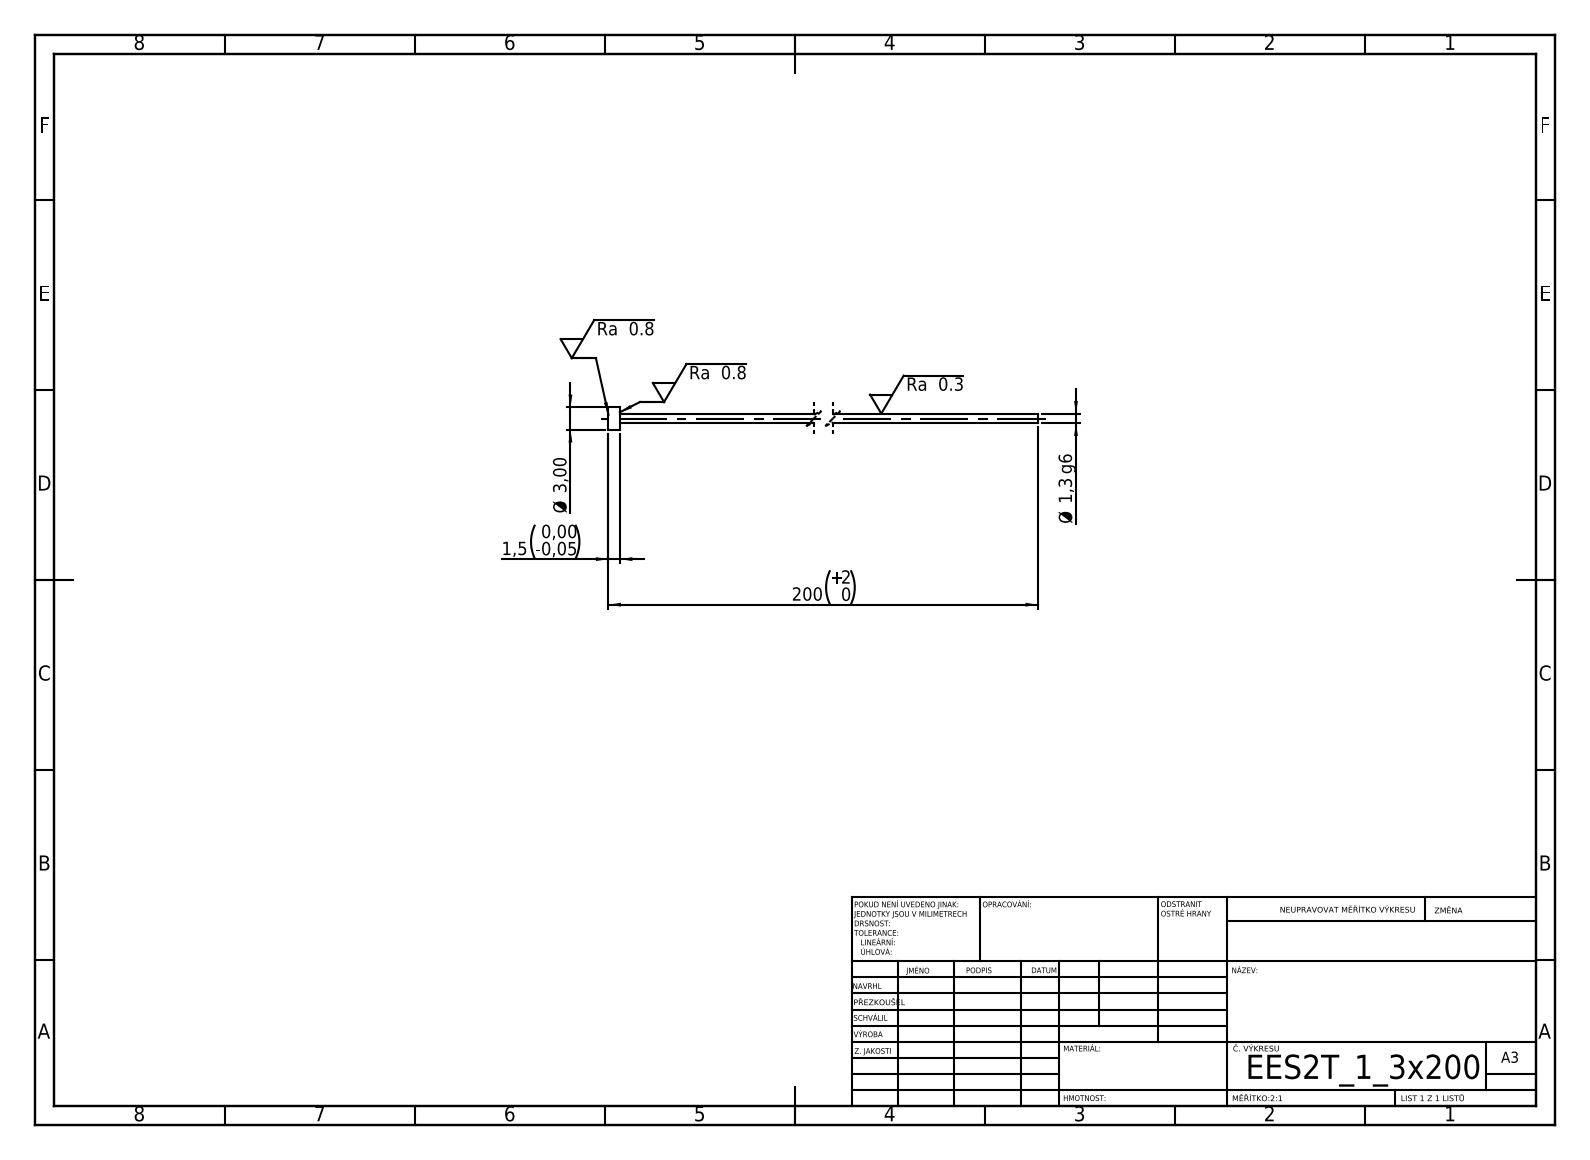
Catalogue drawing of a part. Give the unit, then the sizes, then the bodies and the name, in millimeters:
Units: millimetres
Overall size (bounding box): 200 × 3 × 3
Round bosses / shafts (diameter × count): ⌀3 ×1, ⌀1.3 ×1
Main face-to-face distances: 1.5, 200, 198.5
Volume: 274 mm³ · Surface area: 839 mm²
Bodies: 1 solid, 7 faces (3 planar, 4 cylindrical, 0 other)
STEP written by: SolidWorks 2019 (CONFIG_CONTROL_DESIGN)
